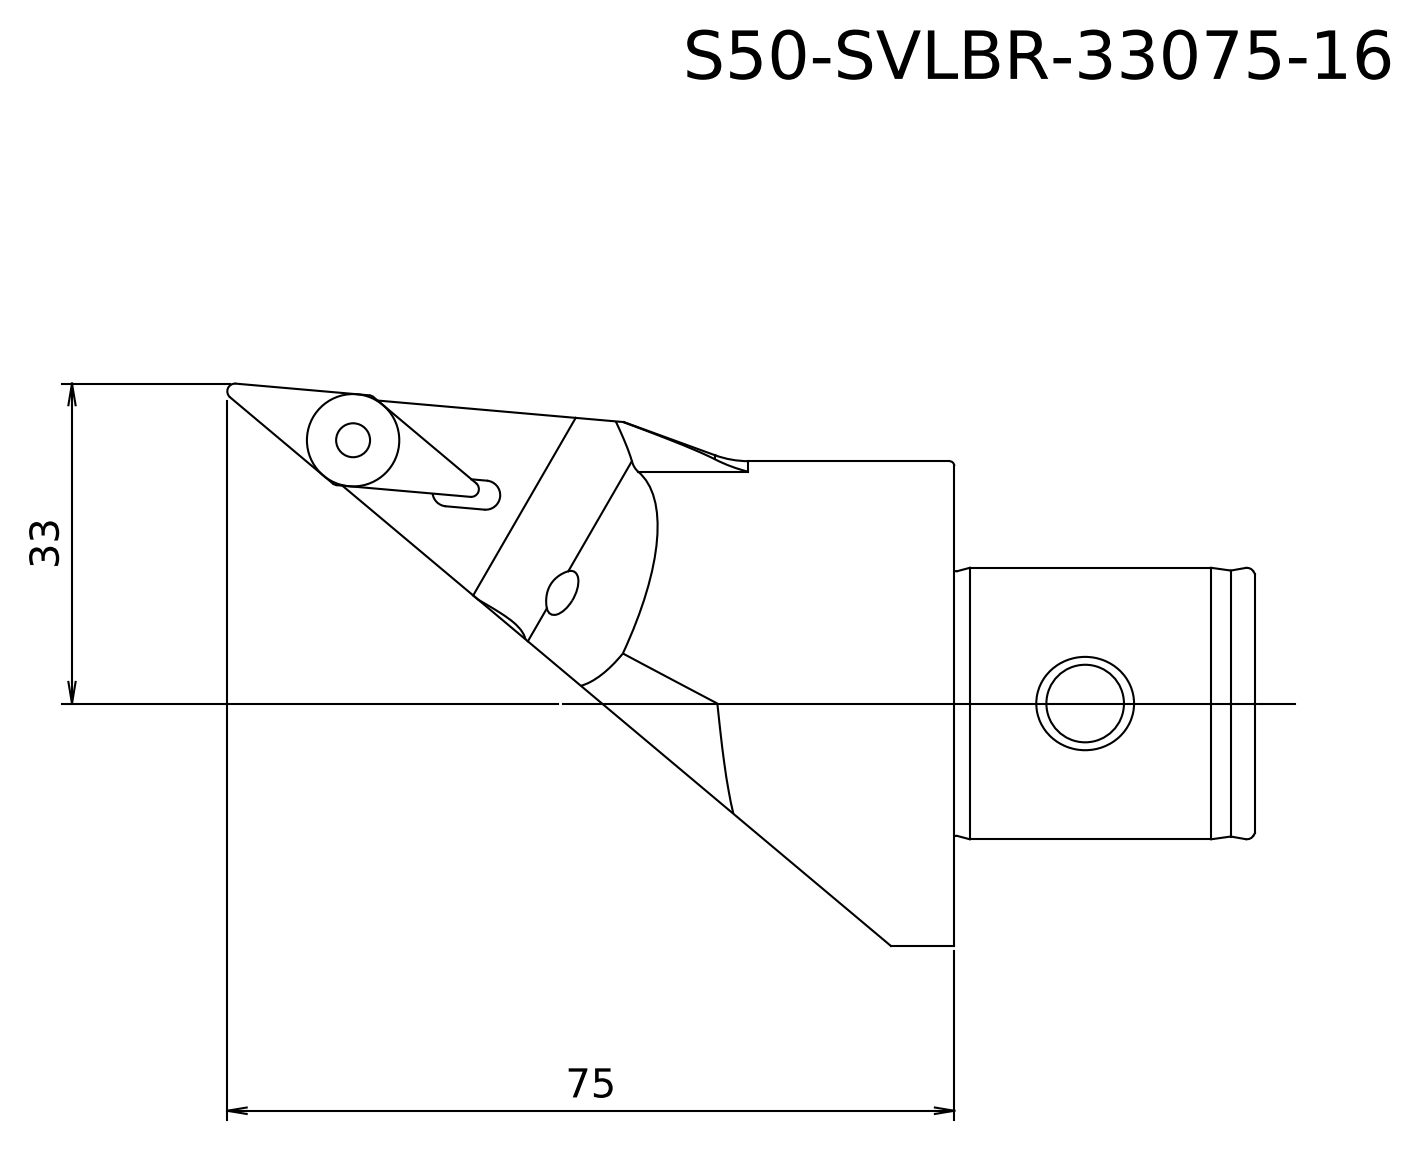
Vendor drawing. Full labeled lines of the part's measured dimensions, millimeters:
STEP written by: Kubotek KeyCreator V8.5.1 (14335) (CONFIG_CONTROL_DESIGN)
Units: millimetres
Bodies: 1 solid, 32 faces (14 planar, 12 cylindrical, 6 other)
Overall size (bounding box): 74.9 × 58 × 53
Volume: 73 587 mm³ · Surface area: 11 239 mm²
Round bosses / shafts (diameter × count): ⌀50 ×1
Partial cylindrical surfaces — rounded edges, fillets, slot ends (radius × count): R10 ×2, R0.4 ×1, R0.8 ×1, R5 ×1, R8 ×1, R39 ×1, R50 ×1
Main face-to-face distances: 0.48, 5.06, 4.76, 9.05, 9.53, 9.52, 9.04, 28.3, 28, 23.24
